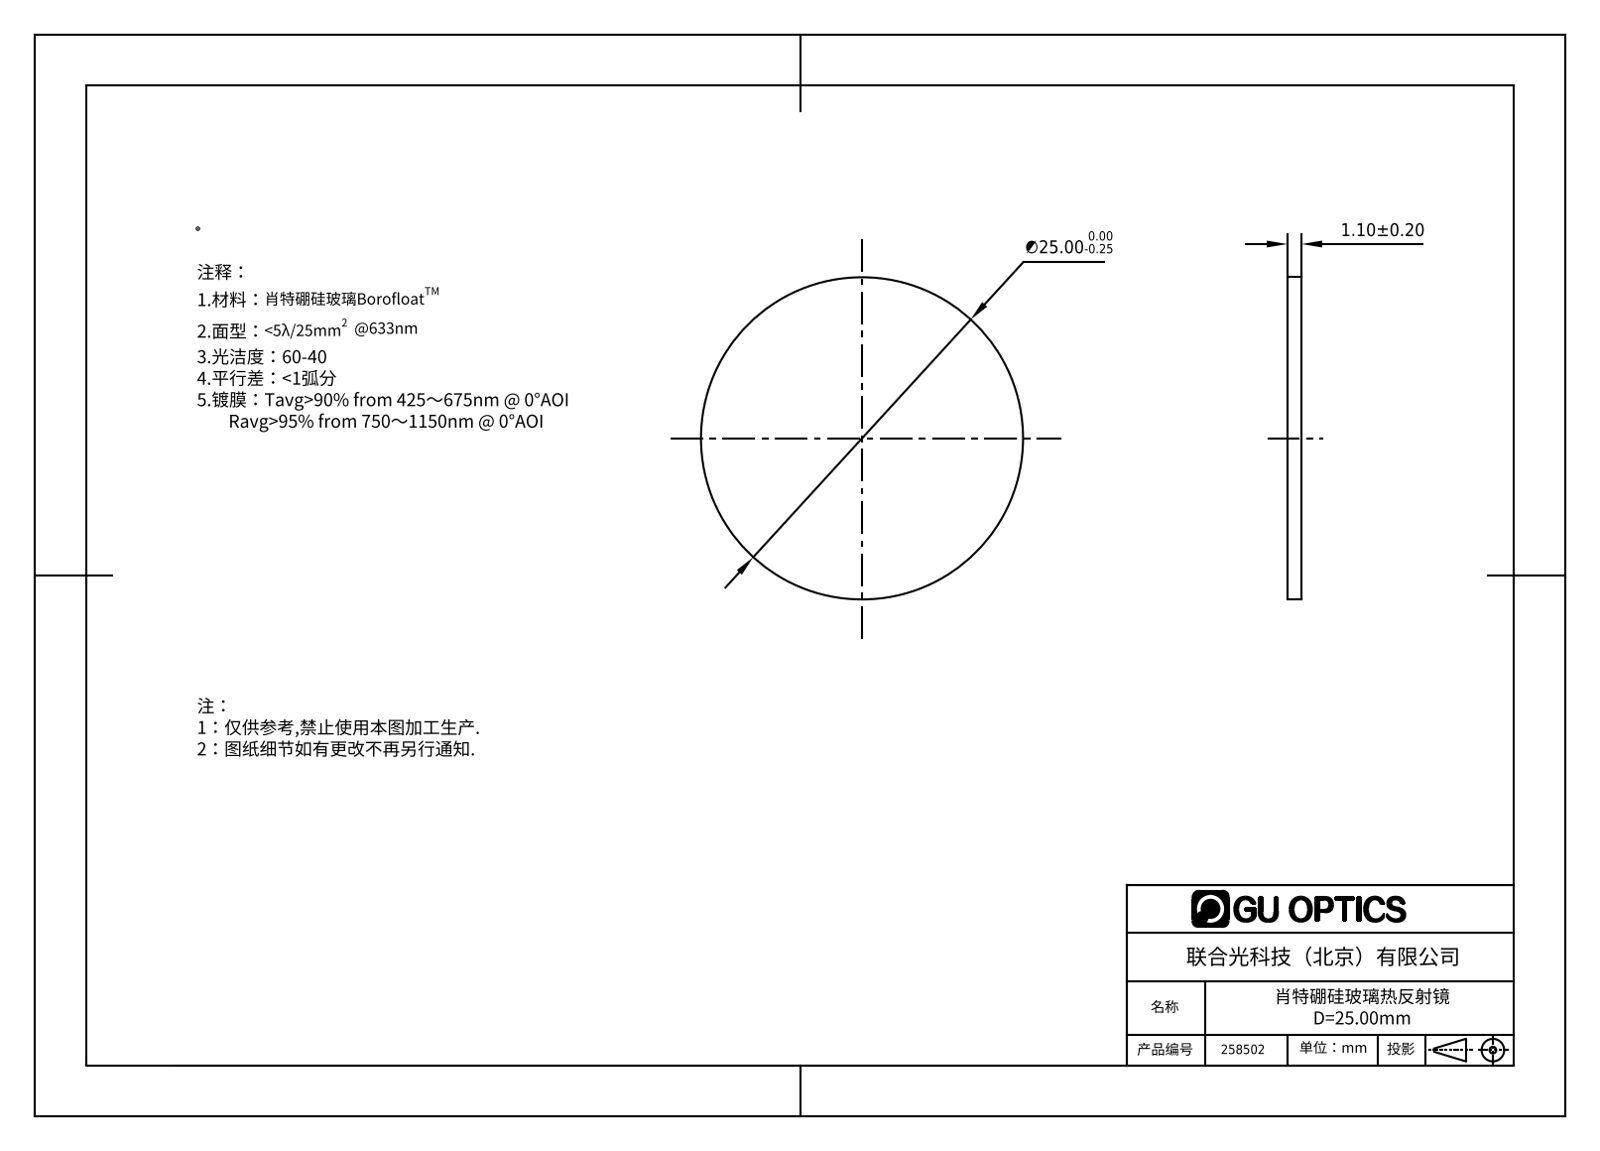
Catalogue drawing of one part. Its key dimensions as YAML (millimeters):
part_name: "258502"
step_written_by: "SolidWorks 2016 (AUTOMOTIVE_DESIGN)"
units: millimeters
bodies: {solids: 1, faces: 4, planar: 2, cylindrical: 2, other: 0}
overall_size: [25, 25, 1.1]
volume: 540
surface_area: 1068
round_bosses_or_shafts:
  - {diameter: 25, count: 1}
face_to_face_distances: [1.1]
